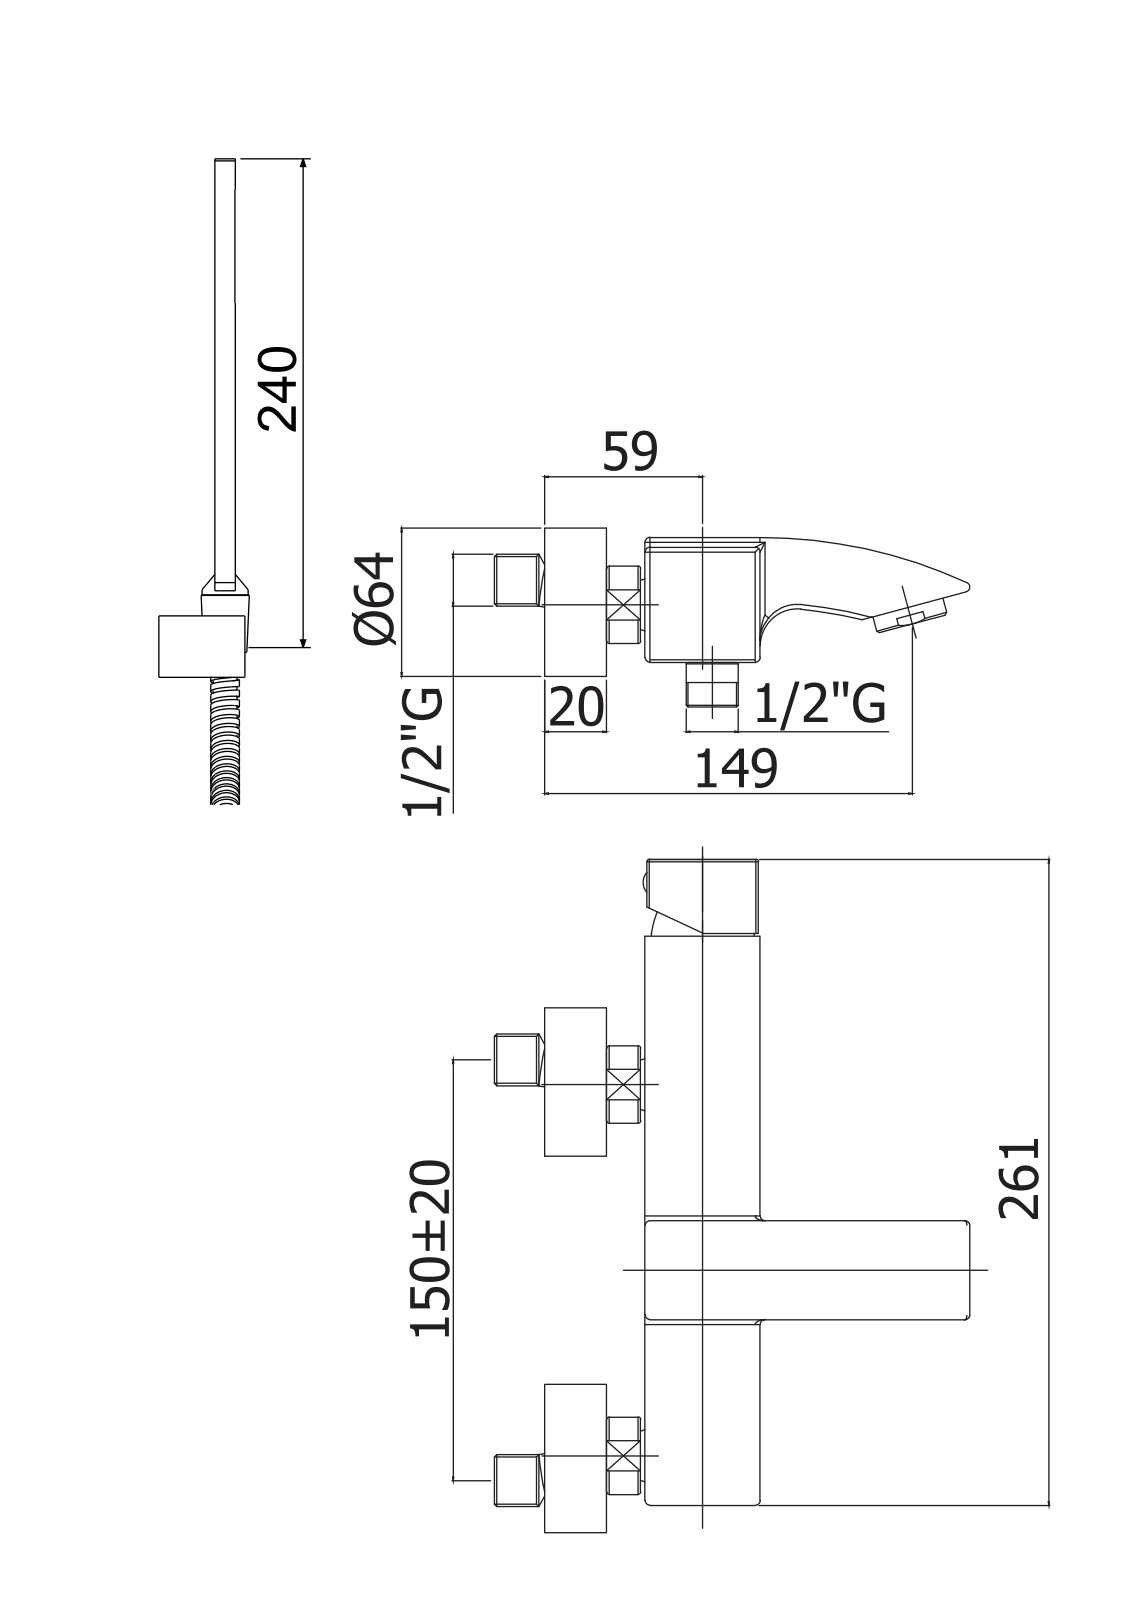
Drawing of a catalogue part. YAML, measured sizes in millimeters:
part_name: "LEC026CR"
step_written_by: "CREO PARAMETRIC BY PTC INC, 2020044 (CONFIG_CONTROL_DESIGN)"
units: millimeters
bodies: {solids: 4, faces: 3299, planar: 2508, cylindrical: 450, other: 341}
overall_size: [379.25, 331.25, 166.24]
volume: 439832
surface_area: 250820
round_holes:
  - {diameter: 7, count: 4}
  - {diameter: 8.5, count: 3}
  - {diameter: 24.5, count: 3}
  - {diameter: 25, count: 3}
  - {diameter: 4, count: 2}
  - {diameter: 4.75, count: 2}
  - {diameter: 10.5, count: 2}
  - {diameter: 11, count: 2}
  - {diameter: 16.5, count: 2}
  - {diameter: 18, count: 2}
  - {diameter: 21, count: 2}
  - {diameter: 21.6, count: 2}
round_bosses_or_shafts:
  - {diameter: 2, count: 11}
  - {diameter: 27, count: 3}
  - {diameter: 24, count: 3}
  - {diameter: 63.5, count: 2}
  - {diameter: 28, count: 2}
  - {diameter: 10, count: 2}
  - {diameter: 37, count: 1}
  - {diameter: 35.5, count: 1}
partial_cylinders:
  - {radius: 0.5, count: 41}
  - {radius: 2, count: 15}
  - {radius: 0.15, count: 11}
  - {radius: 1, count: 10}
  - {radius: 0.3, count: 4}
  - {radius: 4, count: 2}
  - {radius: 15.6, count: 2}
  - {radius: 3, count: 1}
face_to_face_distances: [3.75, 42.75, 46.5, 39, 7.6, 10, 50.35, 3, 54.1, 8]
hole_center_spacings: [7.07, 8.6, 11.4, 4, 6, 10, 13, 14]
